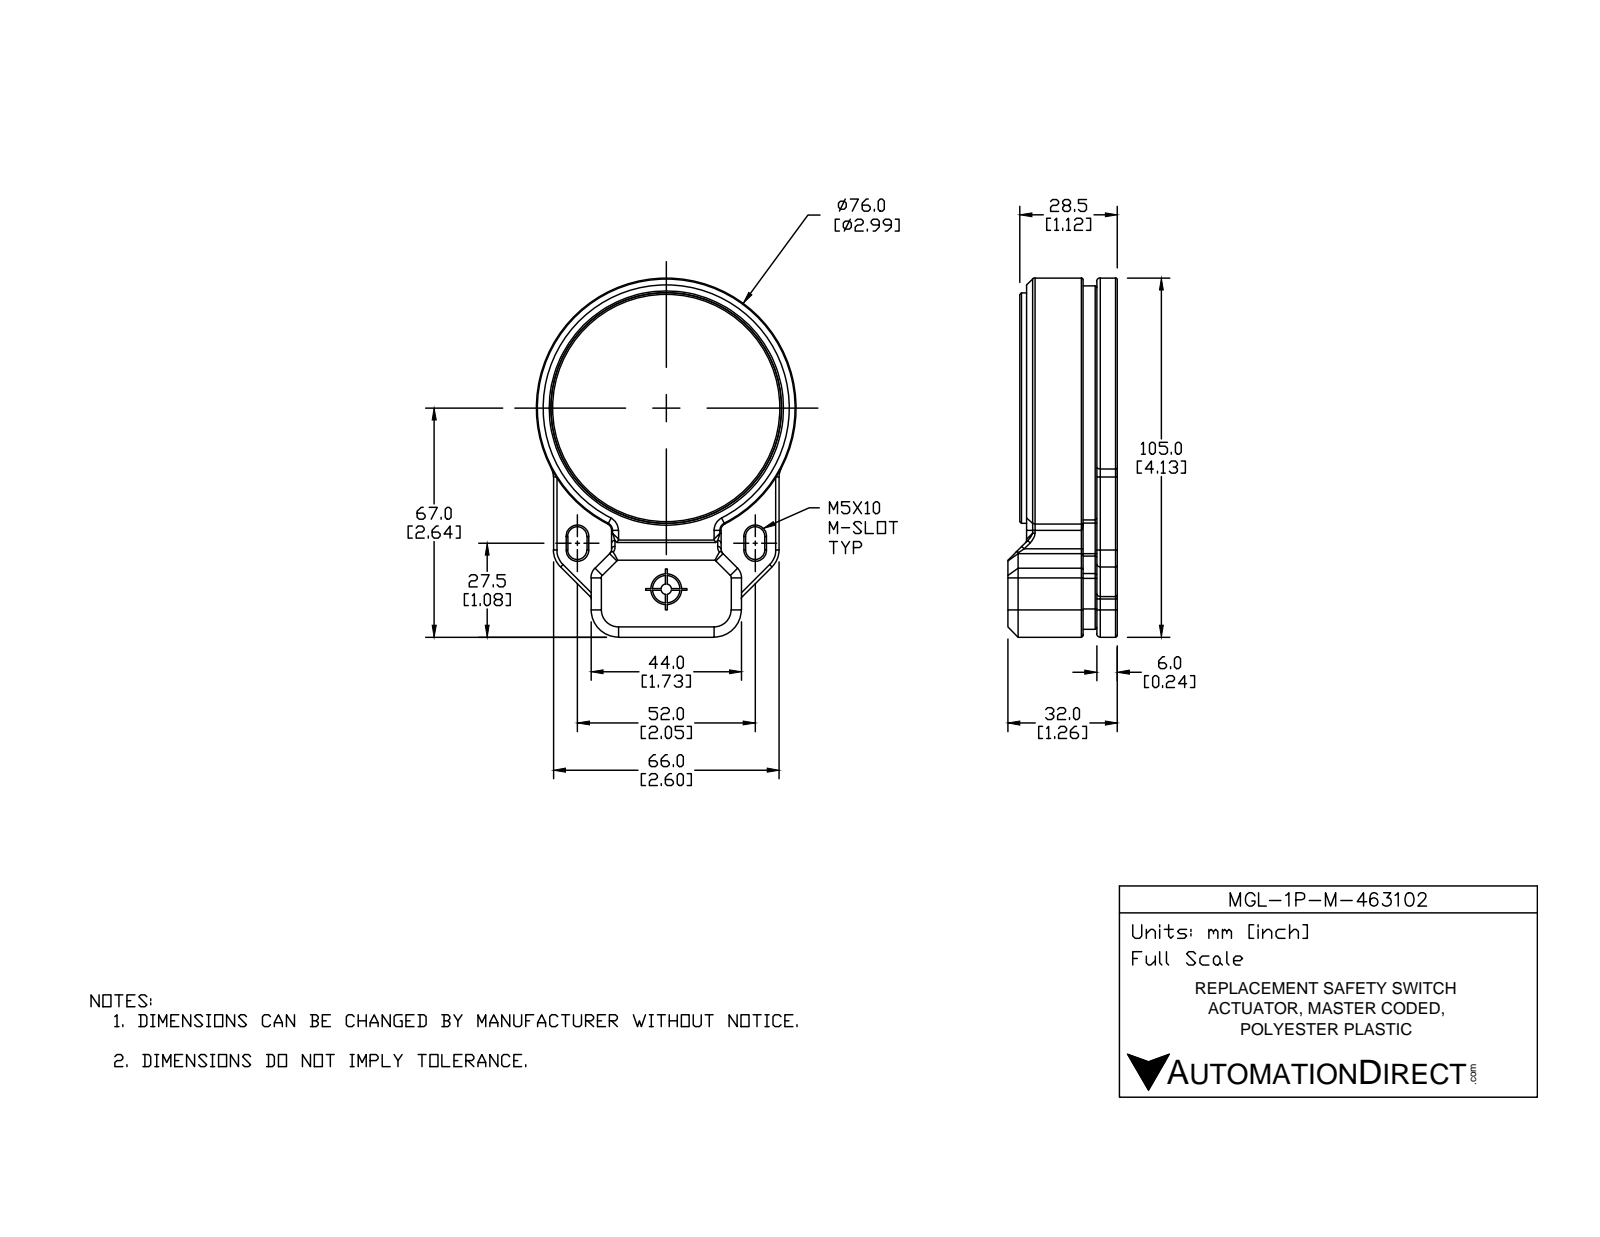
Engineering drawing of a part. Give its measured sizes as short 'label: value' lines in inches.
name: MGL-1P-M-46310
written by: SolidWorks 2017 (AUTOMOTIVE_DESIGN)
unit: in
bodies: 5 solids, 588 faces (139 planar, 240 cylindrical, 209 other)
size: 4.134 × 2.992 × 1.26
volume: 7.179 in³; area: 95.68 in²
holes: 4× ⌀0.453, 2× ⌀0.276, 2× ⌀0.315, 1× ⌀0.266, 1× ⌀0.323, 1× ⌀0.335, 1× ⌀0.354, 1× ⌀0.492, 1× ⌀0.669, 1× ⌀0.827, 1× ⌀1.083, 1× ⌀2.657
bosses: 2× ⌀0.472, 2× ⌀0.315, 1× ⌀2.992, 1× ⌀2.835, 1× ⌀2.811, 1× ⌀2.654, 1× ⌀1.063, 1× ⌀0.63
rounds: 58× R0.02, 44× R0.039, 10× R0.079, 7× R0.024, 4× R0.11, 3× R0.236, 2× R0.157, 2× R0.189
face distances: 0.236, 0.413, 0.65, 0.098, 0.315, 0.059, 0.256, 0.295, 0.551, 0.472
hole spacings: 0.984, 1.392, 0.548, 1.396, 1.969, 2.307, 2.332, 2.34
